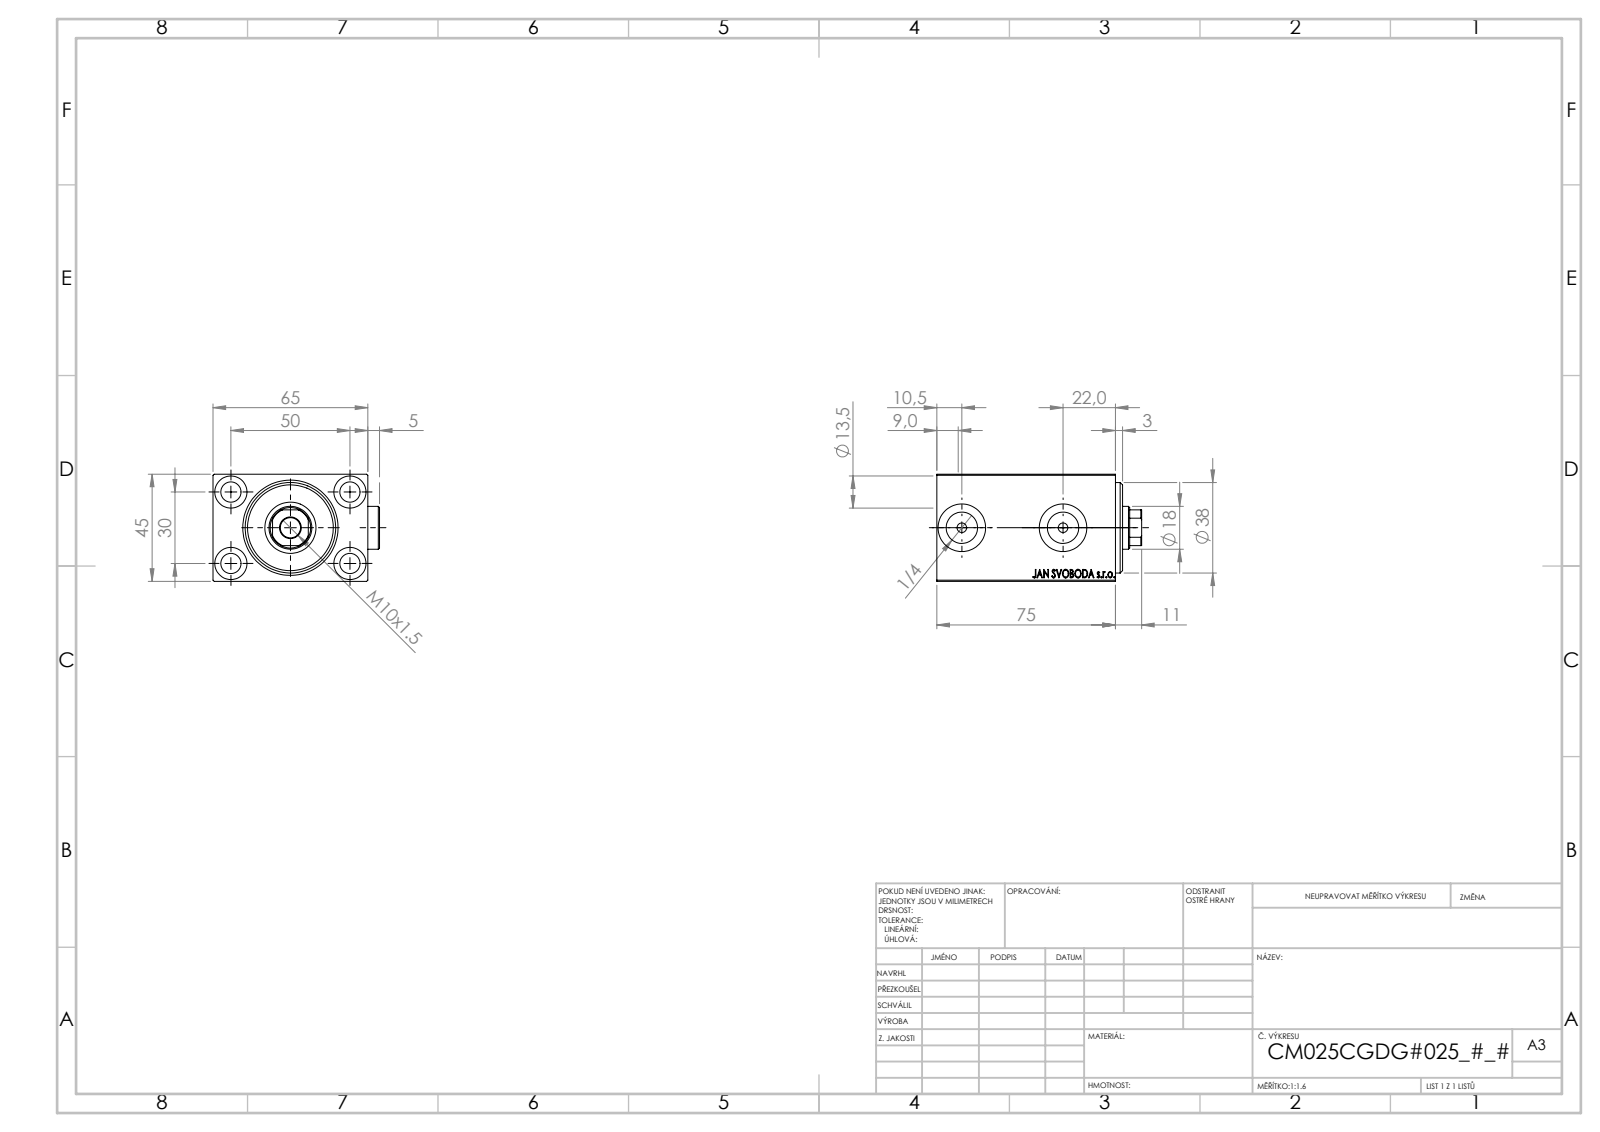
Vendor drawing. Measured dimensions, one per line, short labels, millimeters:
name: V450CM_C_VCP; V450CM_VC_B; Zatka_OIL_PORT; V450CM_C_Body
written by: SolidWorks 2019 (CONFIG_CONTROL_DESIGN)
unit: mm
bodies: 5 solids, 916 faces (442 planar, 76 cylindrical, 398 other)
size: 86 × 69.9 × 45
volume: 188 939 mm³; area: 51 338 mm²
holes: 5× ⌀8.5, 4× ⌀13.5, 2× ⌀4, 2× ⌀13.16, 2× ⌀20, 1× ⌀18, 1× ⌀21.5, 1× ⌀25, 1× ⌀27, 1× ⌀38
bosses: 2× ⌀18
rounds: 1× R8.5
face distances: 45, 65, 5, 6, 64, 69, 64.9, 70, 75, 3
hole spacings: 29.15, 30, 50, 58.31, 42.5
